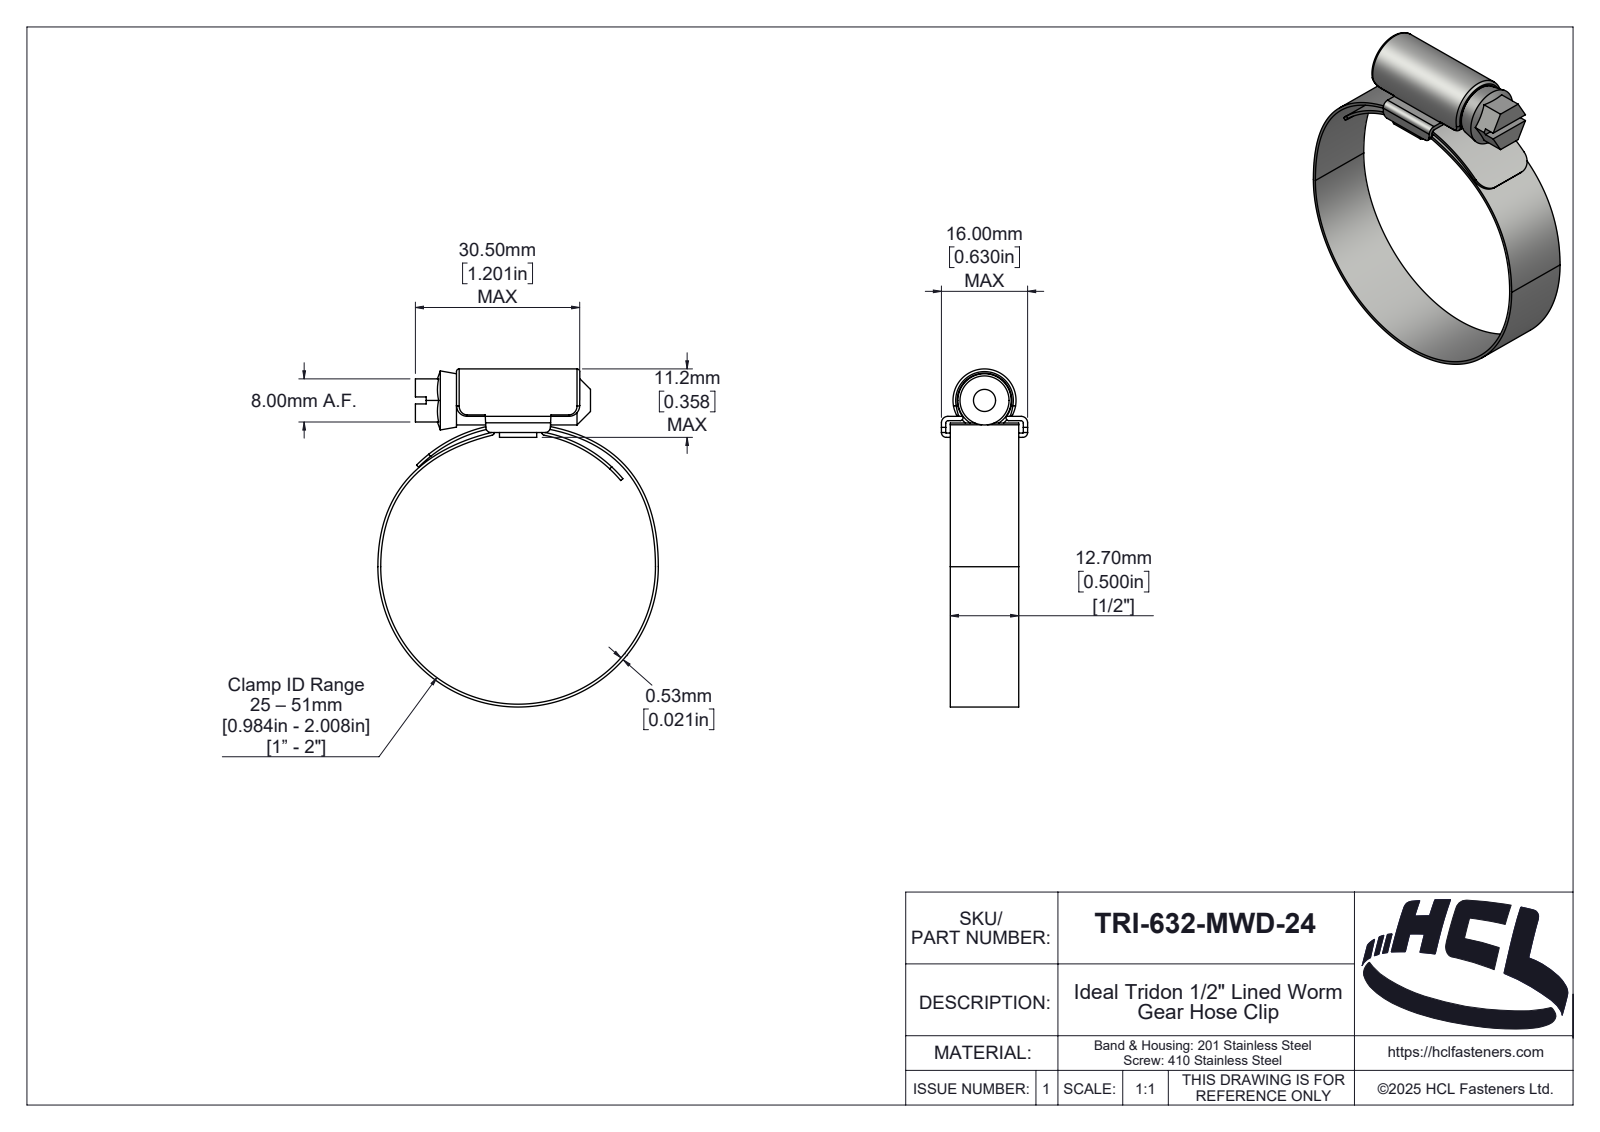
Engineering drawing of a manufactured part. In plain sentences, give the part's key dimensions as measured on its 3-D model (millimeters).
The part is named "TRI-632-MWD-24". Its 3-D file was written by "SolidWorks 2025 (AUTOMOTIVE_DESIGN)". It is 3 solids with 217 faces: 49 planar, 99 cylindrical and 69 other. Overall it measures 62.73 by 52.06 by 16 millimeters. Its volume is 4 046 cubic millimeters and its surface area 8 184 square millimeters. Round bosses or shafts: 1 of diameter 9.1. Partial cylindrical surfaces (rounded edges, fillets, slot ends): 10 of radius 0.5, 4 of radius 3, 2 of radius 0.1, 2 of radius 0.9, 2 of radius 1, 2 of radius 1.03, 2 of radius 1.2, 2 of radius 2. The main face-to-face distances are 0.8, 3.1, 12.7, 2.3, 3.9, 1.65, 14.35, 15.2, 0.85, 13.55.
